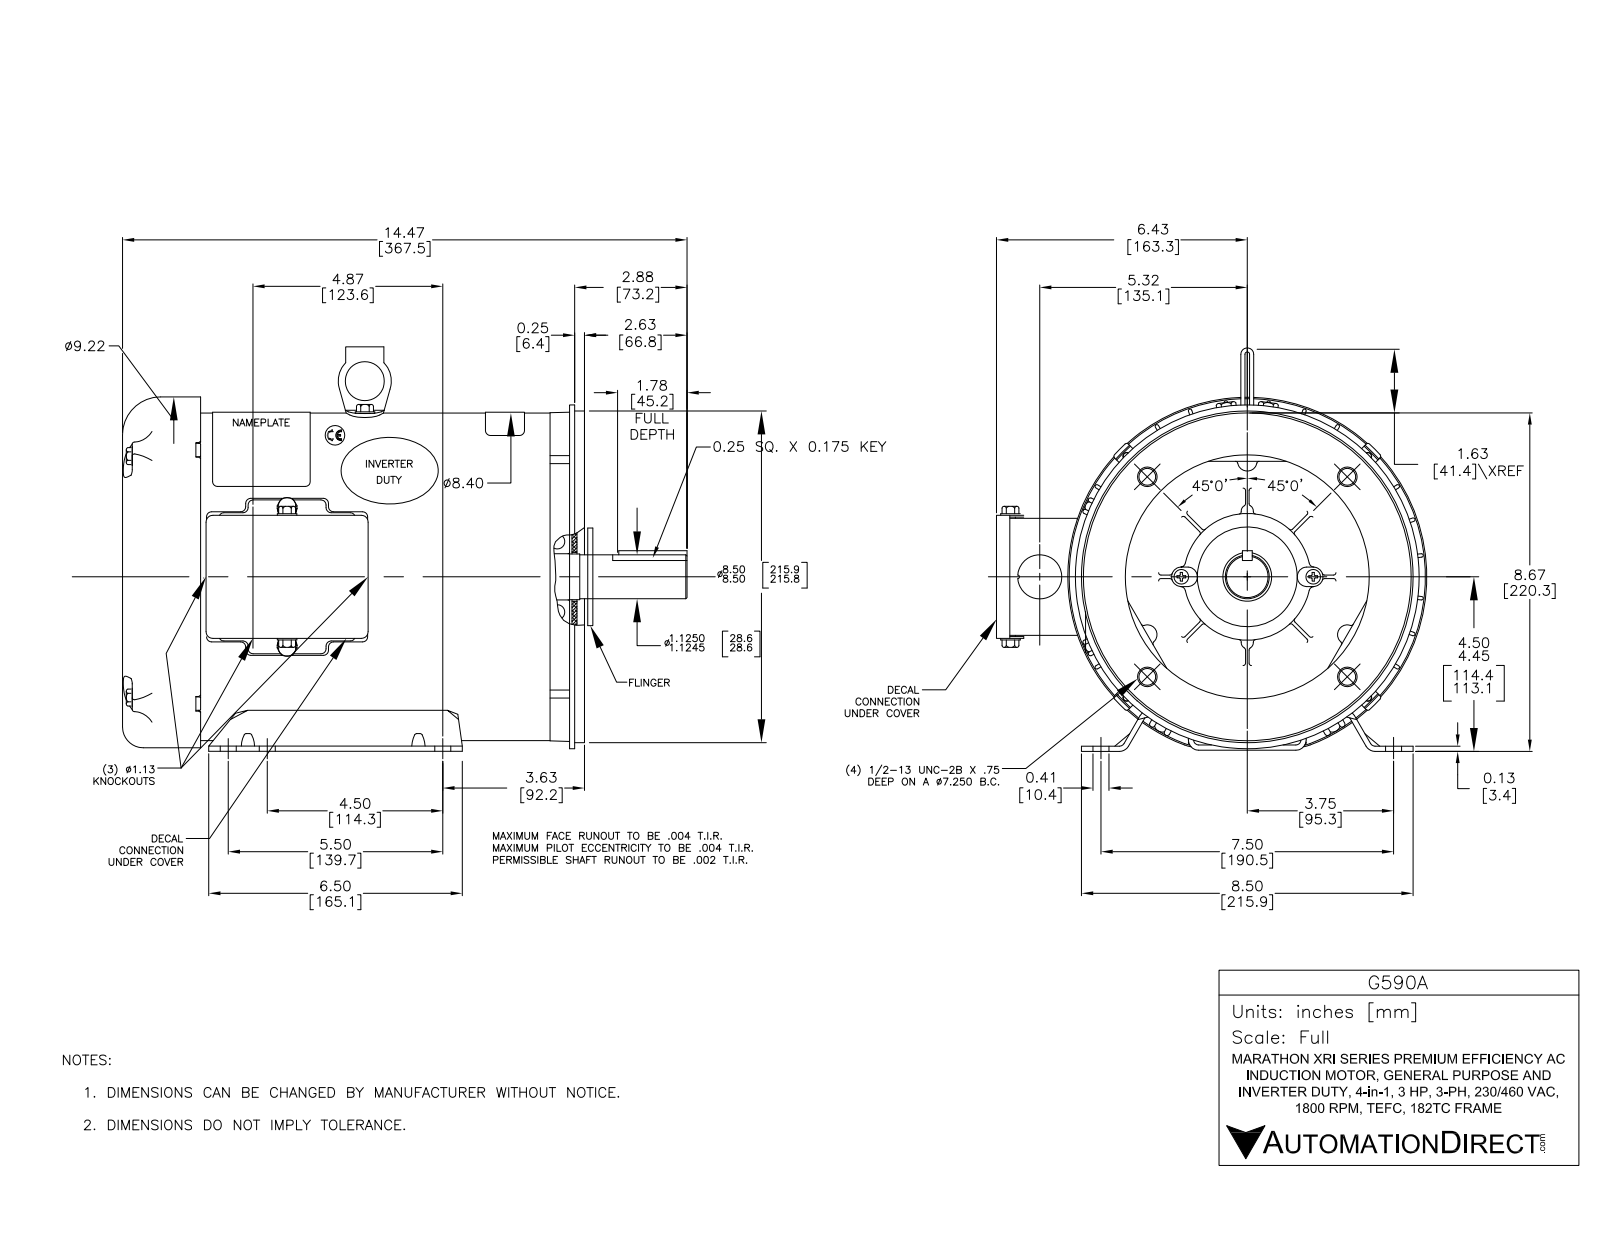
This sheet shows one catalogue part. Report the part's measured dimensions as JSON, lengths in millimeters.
{"part_name": "G590A 1st", "step_written_by": "SolidWorks 2017 (AUTOMOTIVE_DESIGN)", "units": "millimeters", "bodies": {"solids": 33, "faces": 3317, "planar": 942, "cylindrical": 965, "other": 1410}, "overall_size": [367.4, 287.7, 263.2], "volume_mm3": 2238000, "surface_area_mm2": 957400, "round_holes": [[9.7, 8], [5.4, 7], [10.9, 6], [3.9, 4], [5.1, 4], [5.5, 4], [7.1, 4], [10.7, 4], [10.7, 4], [2.6, 2], [5.2, 2], [12.7, 2]], "round_bosses_or_shafts": [[13.2, 10], [6.4, 10], [4.8, 6], [10.5, 4], [9.5, 2], [7.8, 2], [2.8, 2], [234.2, 1]], "partial_cylinders_radius": [[1.5, 90], [2.4, 80], [0.5, 62], [1.1, 25], [3.3, 24], [0.8, 13], [2.2, 8], [6.7, 8]], "face_to_face_distances": [25.4, 1.2, 0.9, 49.1, 23.7, 50, 24.6, 250.8, 276.2, 299.9], "hole_center_spacings": [38.1, 73.2, 78.5, 81.1, 97.9, 116, 124.2, 144.3]}
